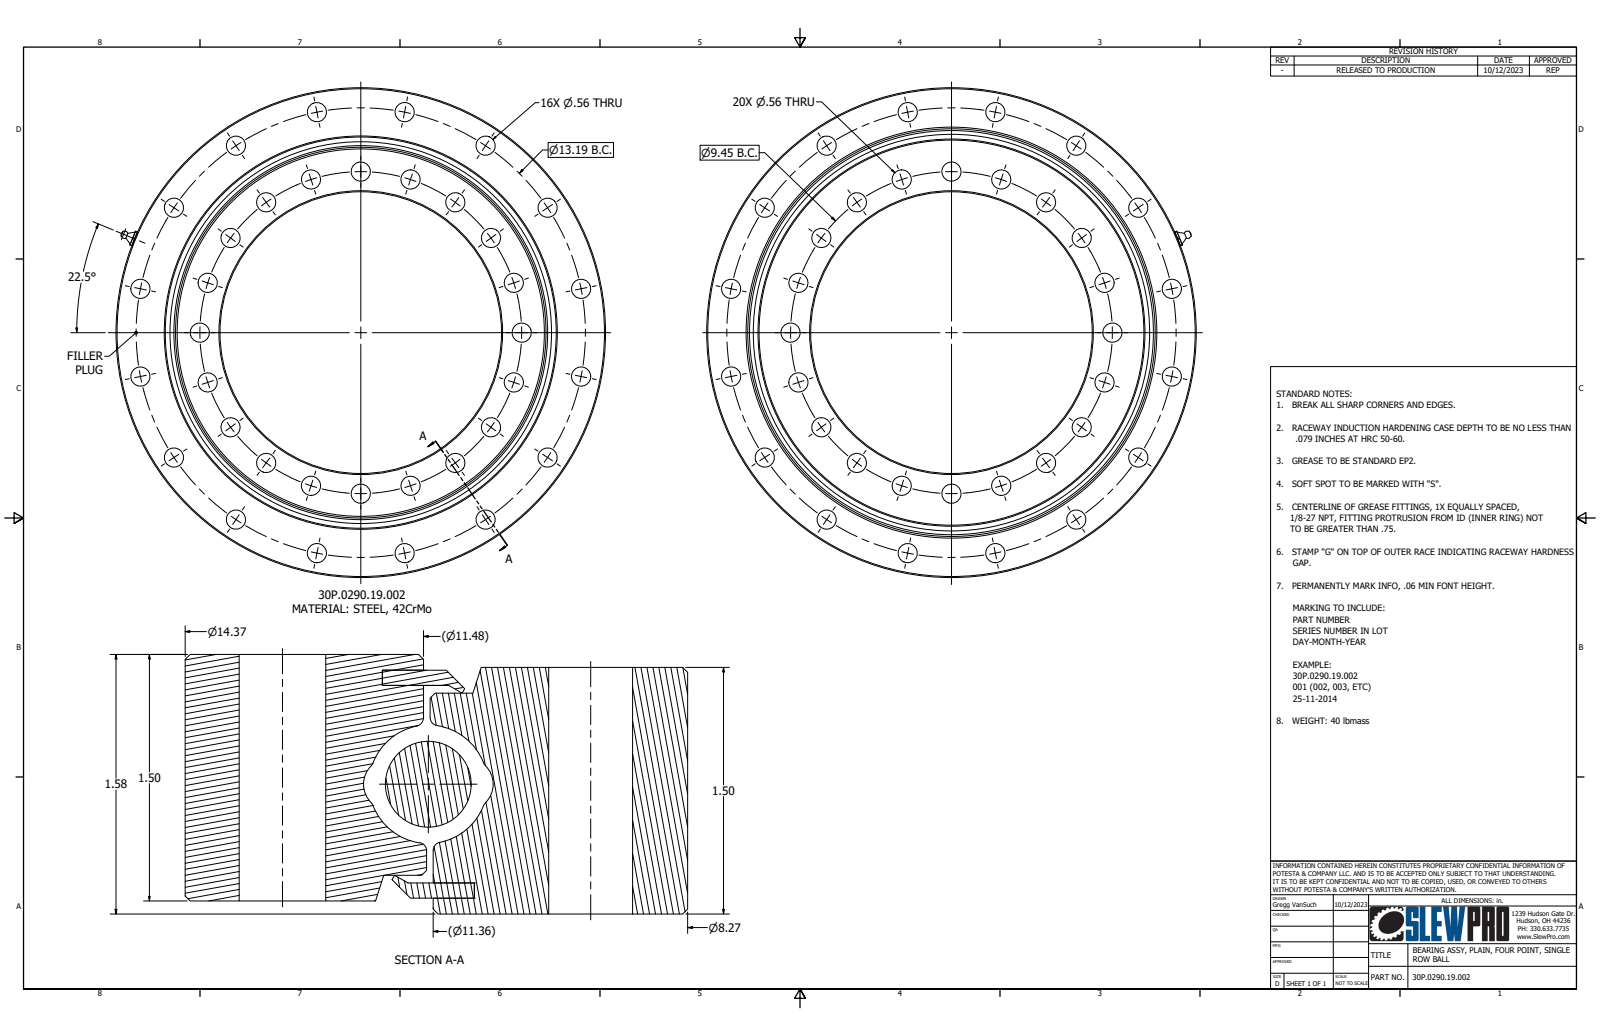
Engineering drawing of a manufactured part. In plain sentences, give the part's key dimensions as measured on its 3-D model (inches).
The part is named "30P.0290.19.002; 1_8 NPT Fitting". Its 3-D file was written by "Autodesk Inventor 2026 (AUTOMOTIVE_DESIGN)". It is 7 solids with 204 faces: 25 planar, 54 cylindrical and 125 other. Overall it measures 14.37 by 14.37 by 1.575 inches. Its volume is 141 cubic inches and its surface area 720.4 square inches. Round holes: 36 of diameter 0.56, 1 of diameter 0.1, 1 of diameter 0.836, 1 of diameter 8.268, 1 of diameter 10.859, 1 of diameter 11.438, 1 of diameter 11.476, 1 of diameter 11.976. Round bosses or shafts: 1 of diameter 14.37, 1 of diameter 11.975, 1 of diameter 11.396, 1 of diameter 11.358, 1 of diameter 10.858, 1 of diameter 0.834. Partial cylindrical surfaces (rounded edges, fillets, slot ends): 1 of radius 5.759. The main face-to-face distances are 1.496, 0.079, 1.291, 1.575, 0.093, 1.417, 0.188, 1.387, 0.109, 1.308. The hole center spacings are 4.724, 6.681, 9.333, 2.92, 7.644, 8.419, 8.987, 9.449.
